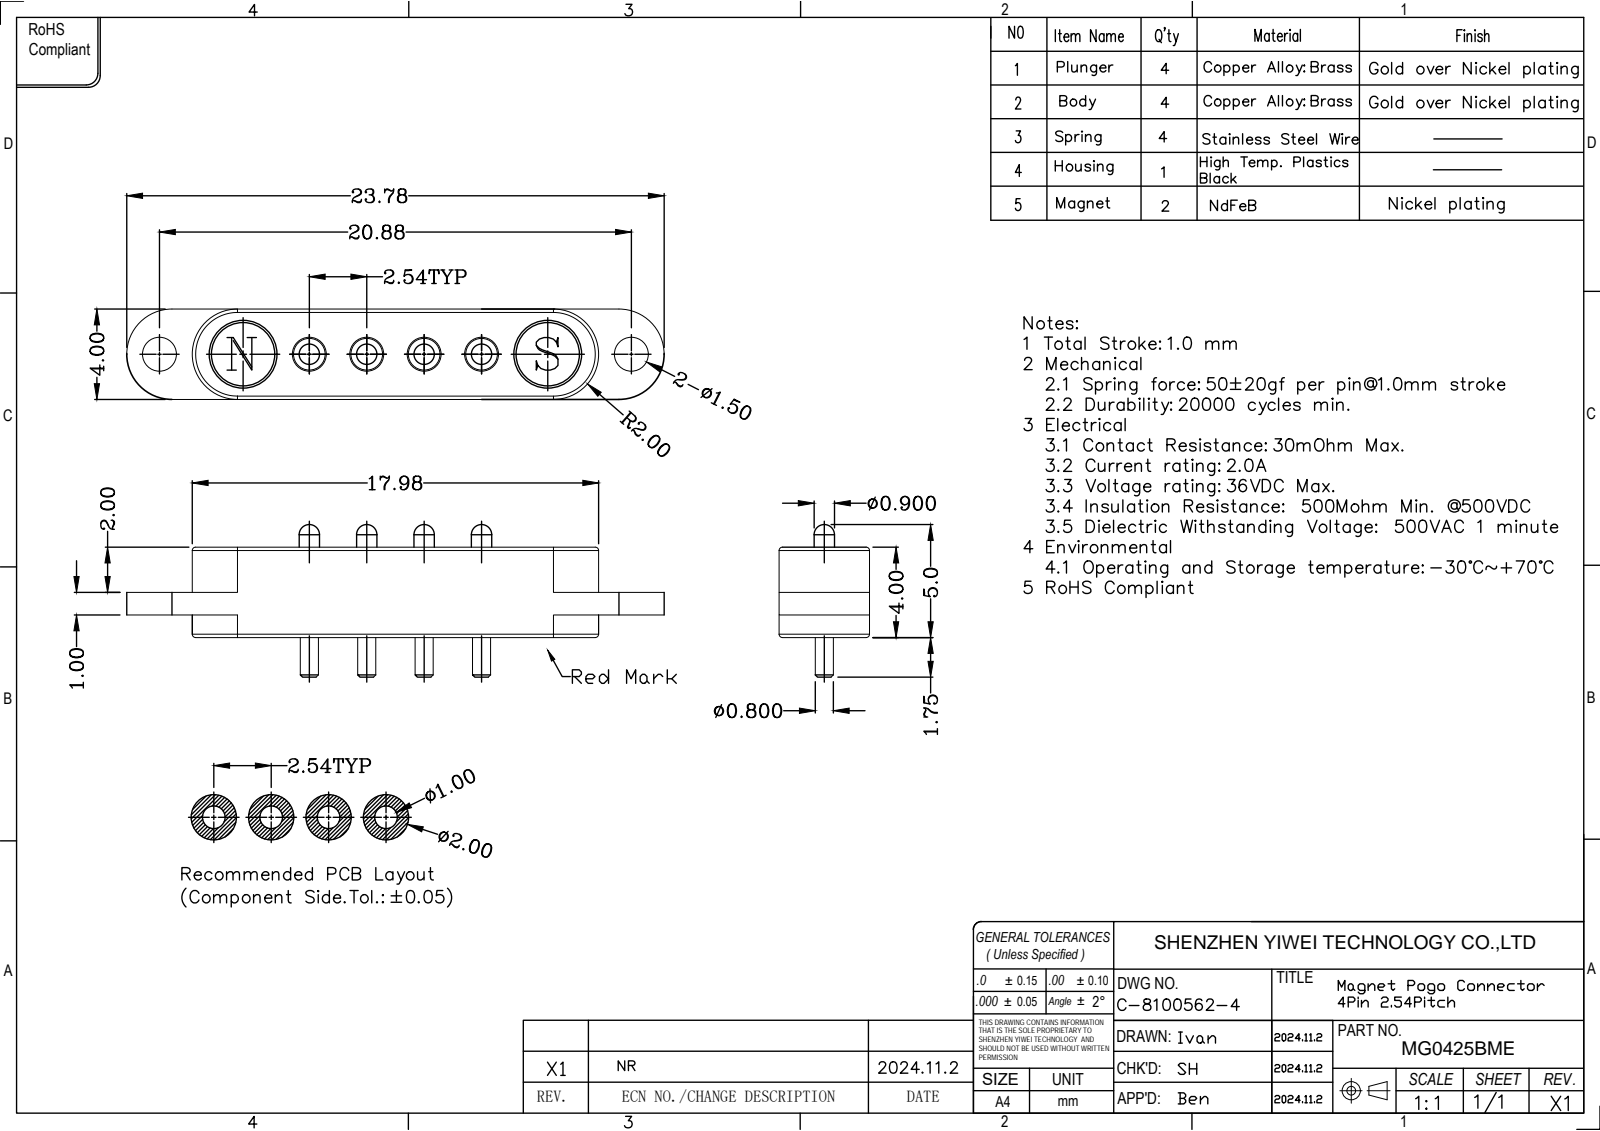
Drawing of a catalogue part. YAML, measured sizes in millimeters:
part_name: "MG3x4; GA18-05015-0818; MG0425B Ear; MG0425BME"
step_written_by: "SolidWorks 2018 (CONFIG_CONTROL_DESIGN)"
units: millimeters
bodies: {solids: 7, faces: 126, planar: 32, cylindrical: 70, other: 24}
overall_size: [23.78, 6.75, 4]
volume: 296
surface_area: 689
round_holes:
  - {diameter: 1.5, count: 6}
  - {diameter: 1.8, count: 4}
  - {diameter: 3, count: 2}
round_bosses_or_shafts:
  - {diameter: 0.9, count: 4}
  - {diameter: 0.8, count: 4}
partial_cylinders:
  - {radius: 2, count: 4}
face_to_face_distances: [4, 1, 2, 3, 0.4, 0.6, 1.6, 3.6, 1.75, 2.15]
hole_center_spacings: [2.54, 2.93, 3.7, 5.08, 5.47, 6.63, 8.01, 9.17]
